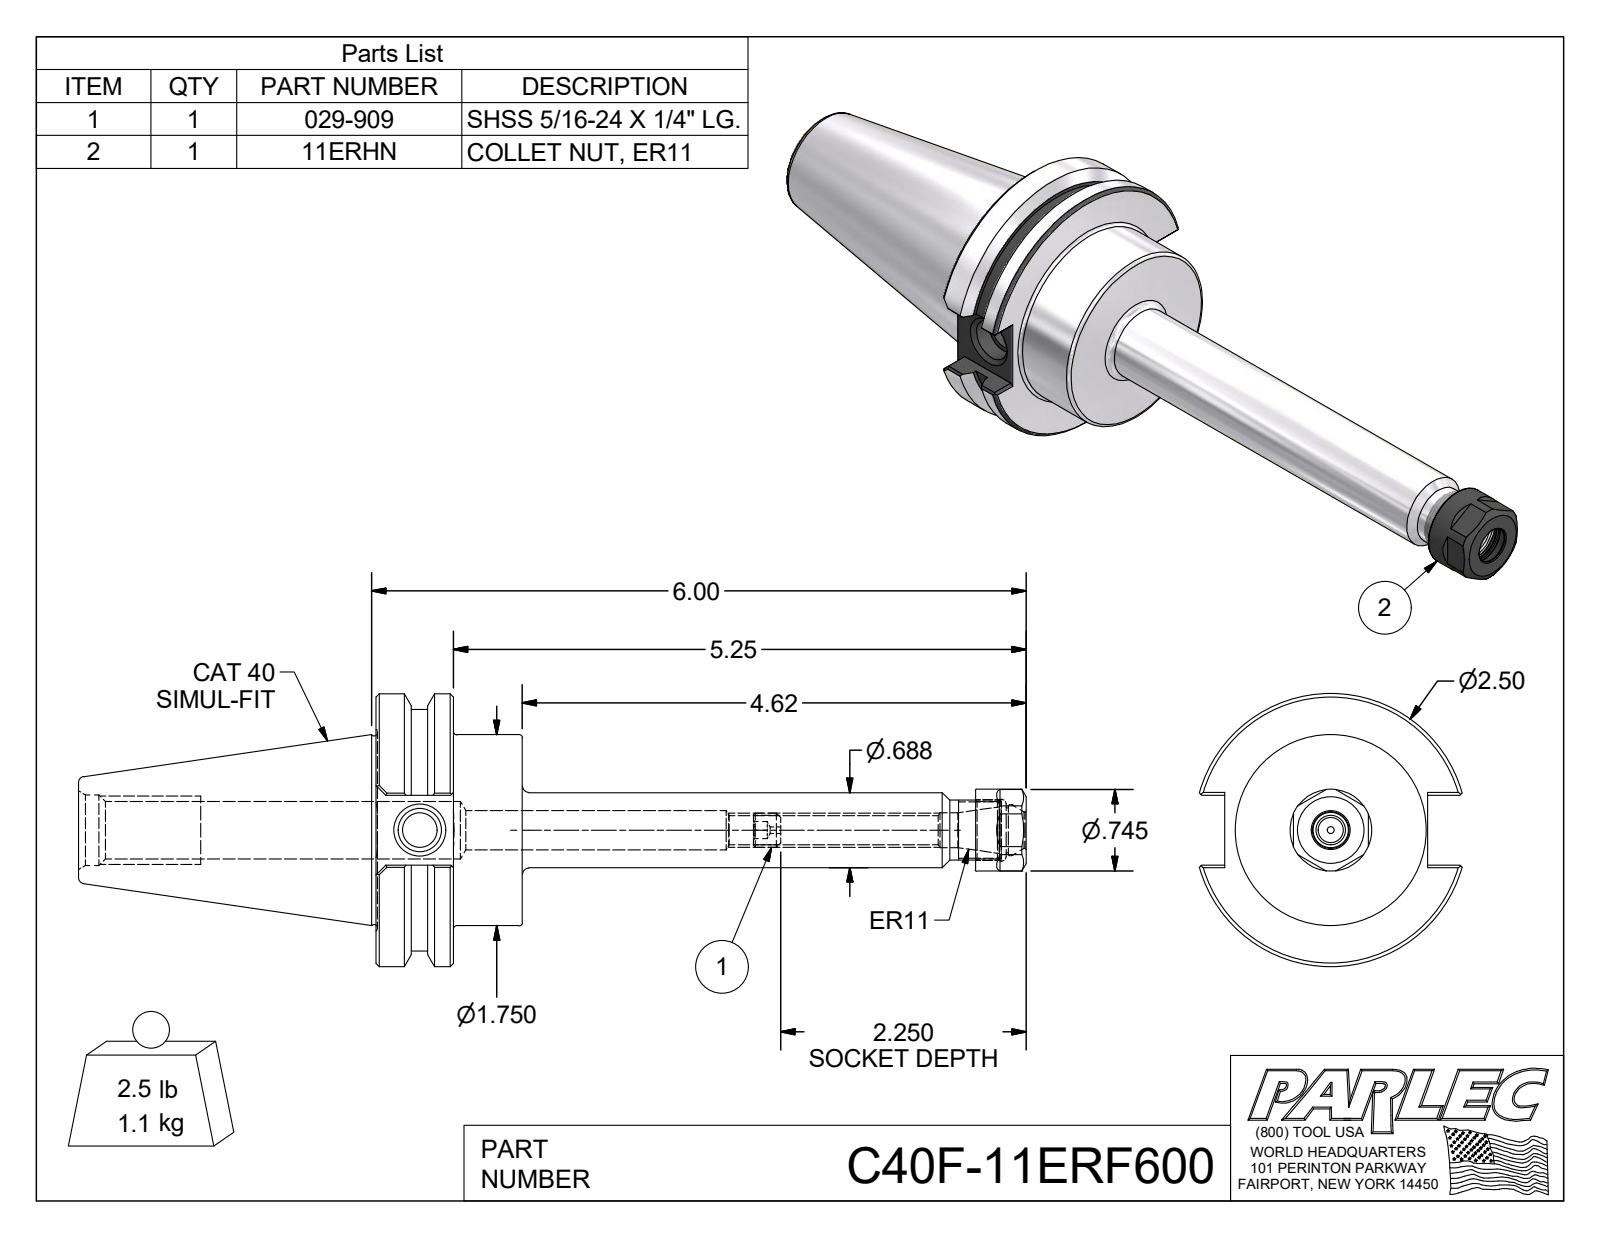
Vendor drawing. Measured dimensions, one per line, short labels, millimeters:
name: C40F-11ERF600; 029-909; 11ERHN
written by: Autodesk Inventor 2016 (AUTOMOTIVE_DESIGN)
unit: mm
bodies: 3 solids, 135 faces (62 planar, 23 cylindrical, 50 other)
size: 220.66 × 63.5 × 61.11
volume: 148 633 mm³; area: 33 750 mm²
holes: 1× ⌀1.52, 1× ⌀6.78, 1× ⌀8, 1× ⌀8.13, 1× ⌀8.51, 1× ⌀9.14, 1× ⌀10.13, 1× ⌀11.81, 1× ⌀13.33, 1× ⌀13.39, 1× ⌀14.35, 1× ⌀16.46
bosses: 1× ⌀63.5, 1× ⌀56.26, 1× ⌀44.45, 1× ⌀19.05, 1× ⌀17.48, 1× ⌀14, 1× ⌀7.94
face distances: 16, 18.04, 34.04, 47.25, 16.26, 151.39, 133.35, 117.35, 69.27, 87.31
